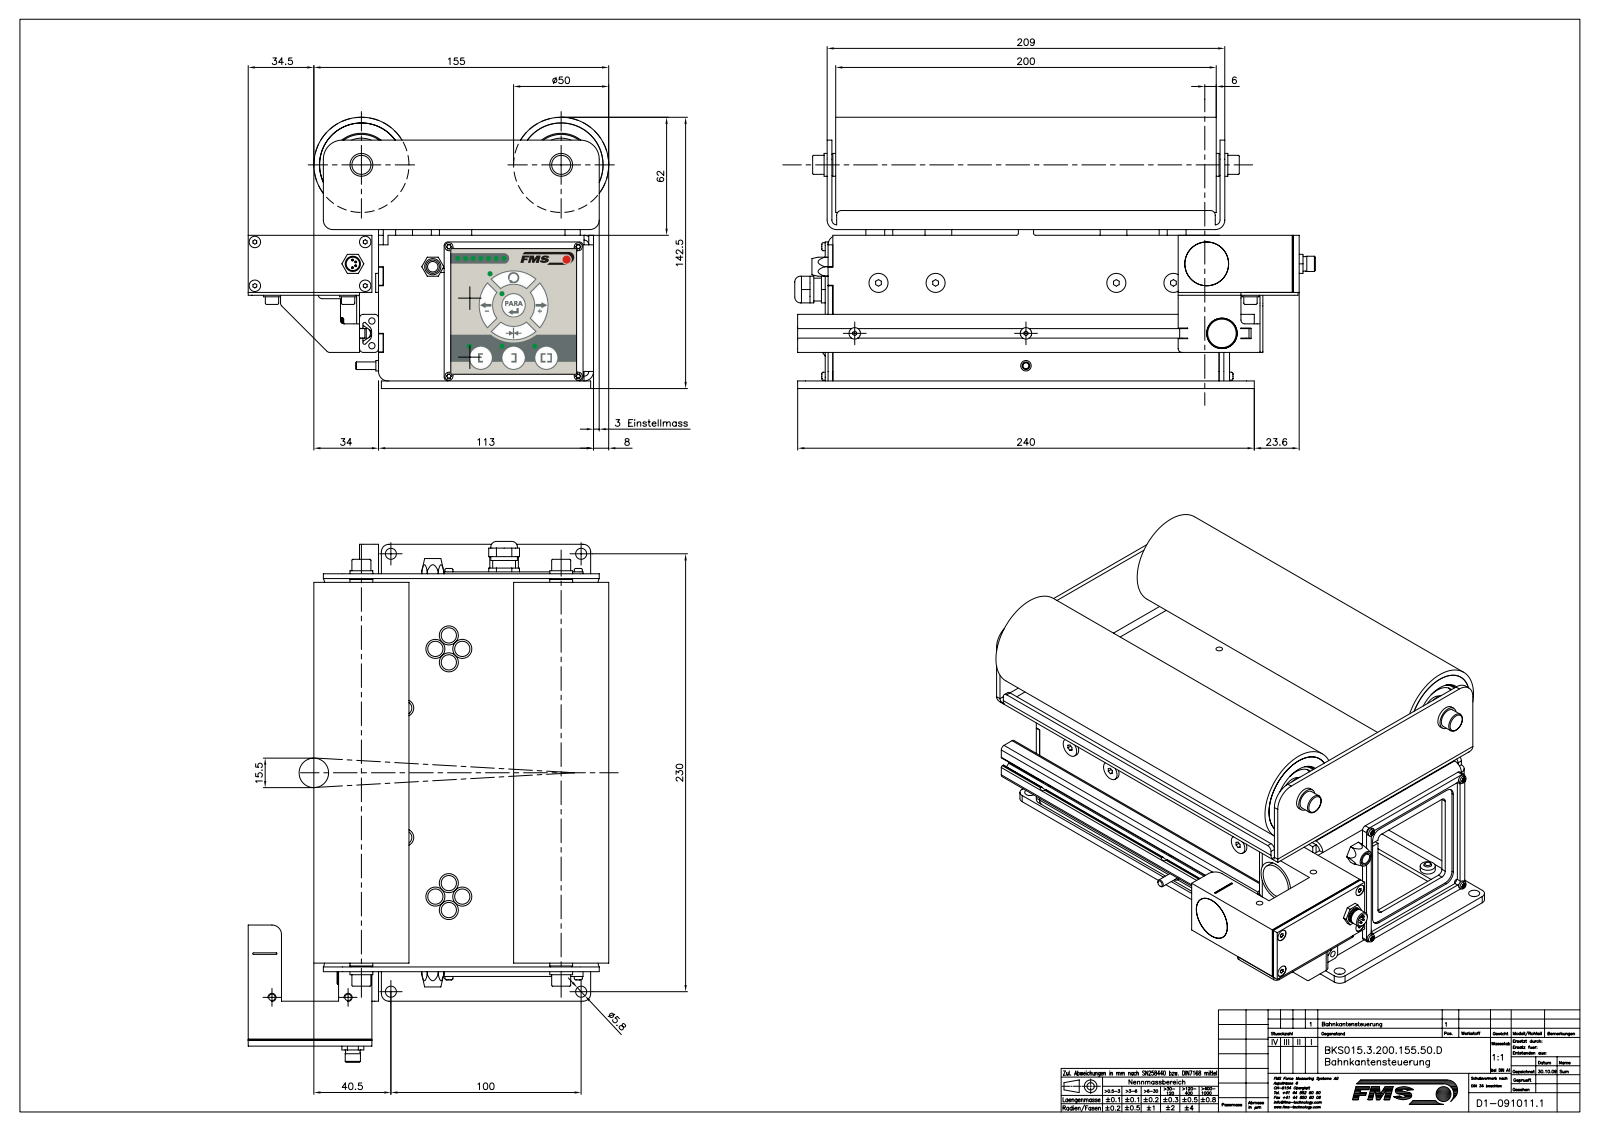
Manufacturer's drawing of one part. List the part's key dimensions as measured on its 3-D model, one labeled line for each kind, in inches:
Part name (STEP PRODUCT): K0910111; K0910115; K0910114; K0901207 (+8 more)
STEP written by: Mechanical Desktop 2007 (CONFIG_CONTROL_DESIGN)
Units: inches
Bodies: 129 solids, 2841 faces (1315 planar, 1178 cylindrical, 348 other)
Overall size (bounding box): 10.791 × 7.461 × 5.61
Volume: 50.54 in³ · Surface area: 875 in²
Round holes (diameter × count): ⌀0.126 ×18, ⌀0.177 ×13, ⌀0.236 ×10, ⌀0.209 ×9, ⌀0.098 ×8, ⌀0.084 ×7, ⌀0.102 ×7, ⌀0.213 ×7, ⌀0.169 ×5, ⌀0.075 ×4, ⌀0.134 ×4, ⌀0.135 ×4
Round bosses / shafts (diameter × count): ⌀0.315 ×19, ⌀0.157 ×17, ⌀0.394 ×15, ⌀0.197 ×13, ⌀0.311 ×7, ⌀0.177 ×7, ⌀0.118 ×7, ⌀0.098 ×7
Partial cylindrical surfaces — rounded edges, fillets, slot ends (radius × count): R0.01 ×48, R0.098 ×29, R0.197 ×27, R0.079 ×21, R0.039 ×10, R0.315 ×9, R0.124 ×8, R0.118 ×7
Main face-to-face distances: 0.098, 0.157, 0.079, 3.13, 8.11, 3.228, 4.35, 3.287, 3.386, 0.02
Hole centre spacings: 0.394, 2.606, 2.677, 0.103, 0.463, 0.557, 1.194, 1.79
